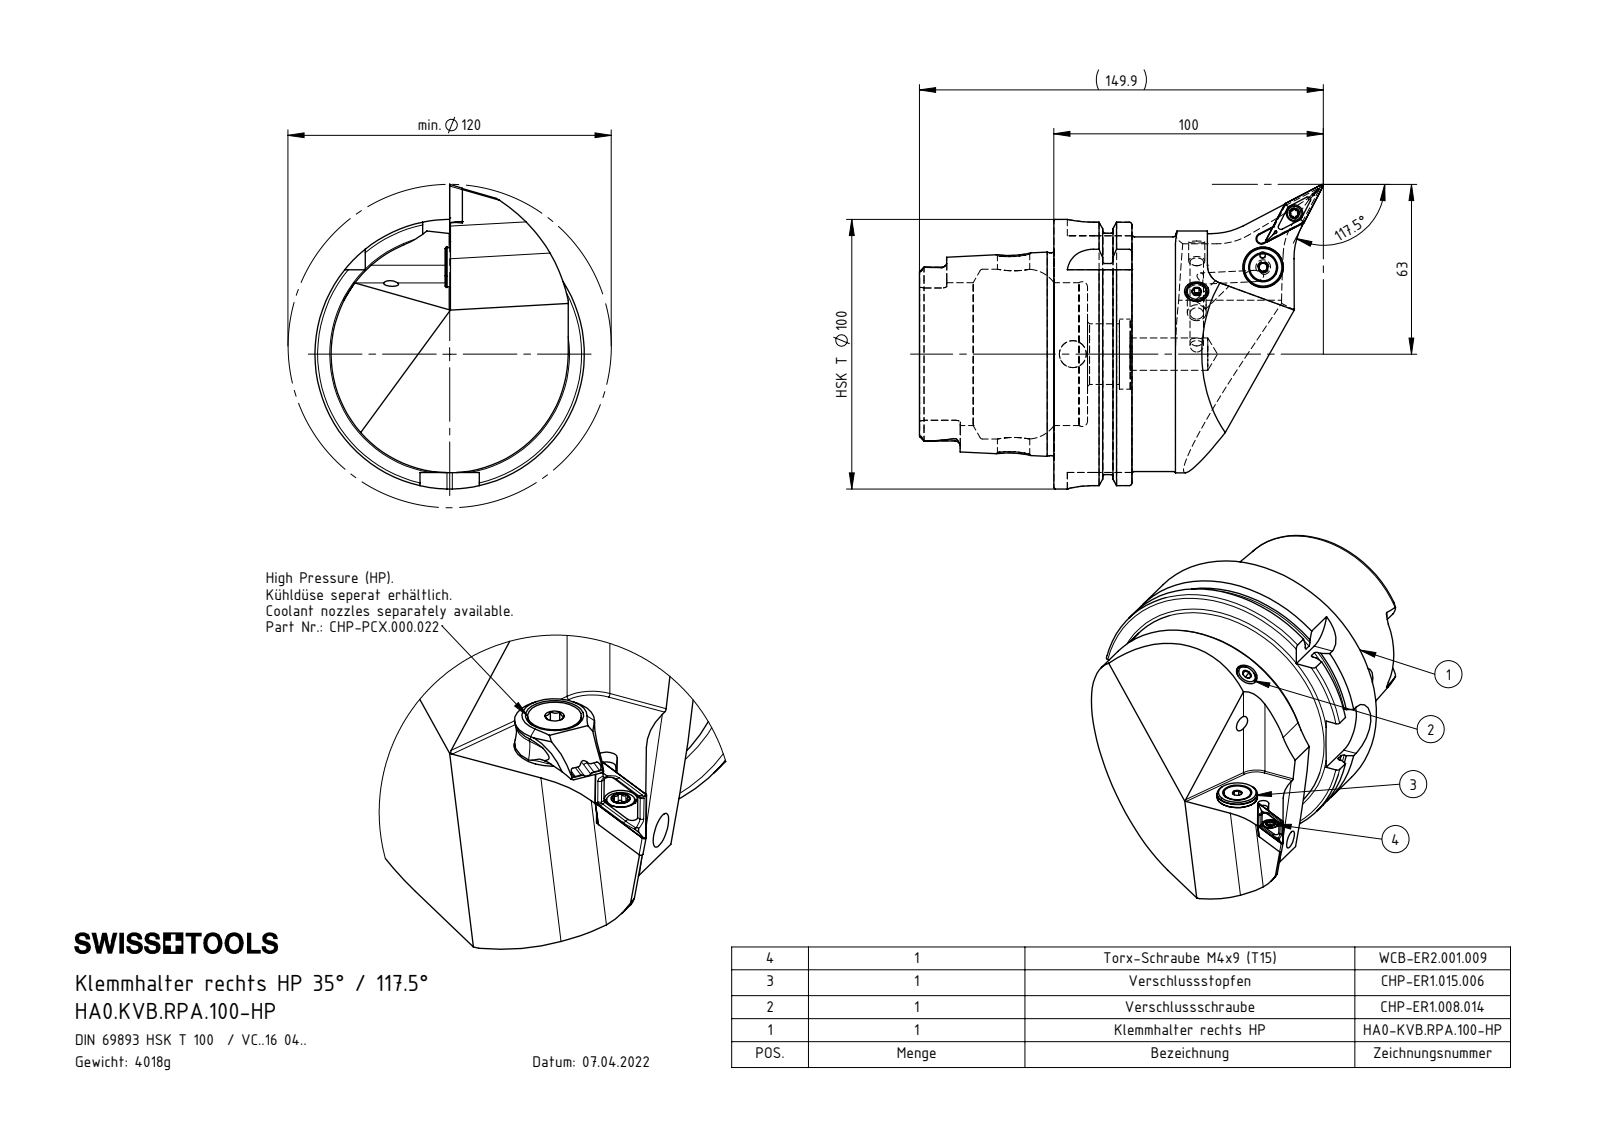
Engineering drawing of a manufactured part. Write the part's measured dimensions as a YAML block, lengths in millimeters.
part_name: "CHP-ER1.015.006; KV..RPA.100-HP; DIN 7991 - M5x15; DIN 3771 - 13x1 (+7 more)"
step_written_by: "SolidWorks 2017 (AUTOMOTIVE_DESIGN)"
units: millimeters
bodies: {solids: 9, faces: 236, planar: 59, cylindrical: 55, other: 122}
overall_size: [147.99, 100.87, 77.05]
volume: 2436
surface_area: 12396
round_holes:
  - {diameter: 1.2, count: 1}
  - {diameter: 2.5, count: 1}
  - {diameter: 3, count: 1}
  - {diameter: 4.4, count: 1}
  - {diameter: 5, count: 1}
  - {diameter: 5.2, count: 1}
  - {diameter: 6.1, count: 1}
round_bosses_or_shafts:
  - {diameter: 15, count: 1}
  - {diameter: 13.4, count: 1}
  - {diameter: 10, count: 1}
  - {diameter: 8, count: 1}
  - {diameter: 6, count: 1}
  - {diameter: 5.5, count: 1}
  - {diameter: 5.25, count: 1}
  - {diameter: 5, count: 1}
partial_cylinders:
  - {radius: 0.34, count: 6}
  - {radius: 0.59, count: 6}
face_to_face_distances: [6.5, 6.4, 6.36, 6.46, 4.8, 4.76, 1.6, 1.7, 3, 3.25]
hole_center_spacings: [2.25, 4.49, 4.5, 18.72, 19.58, 23.22]
